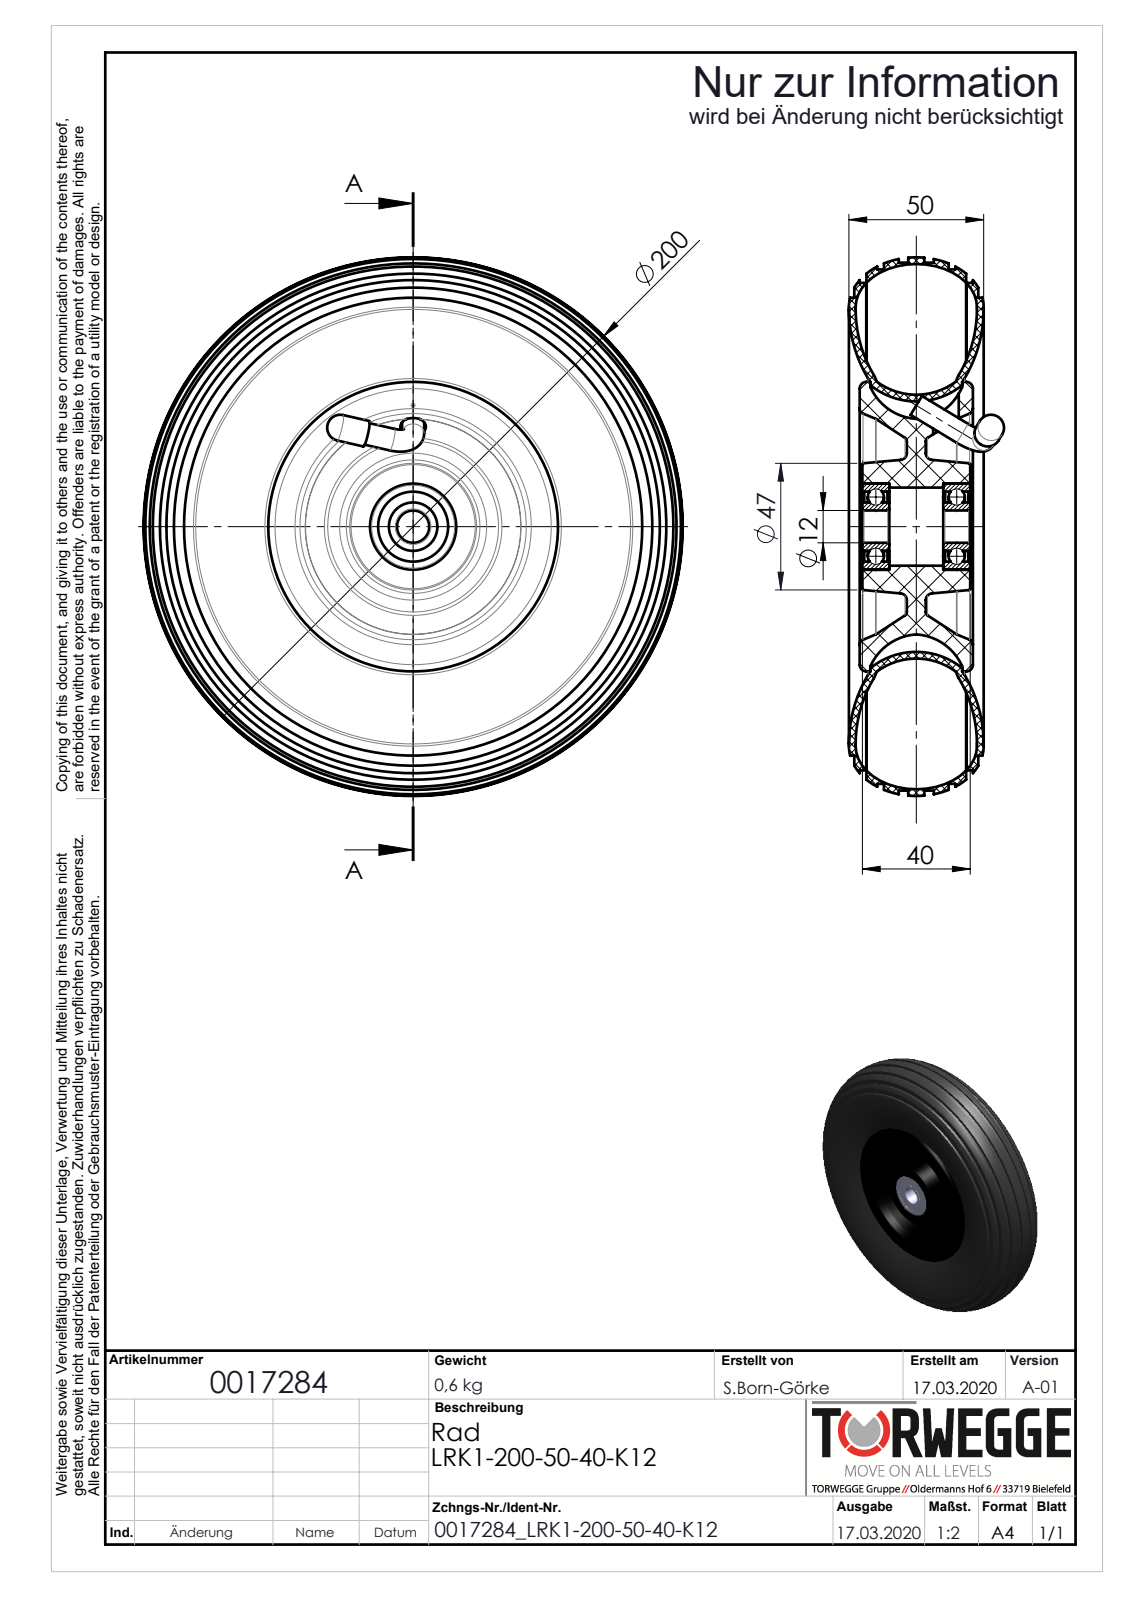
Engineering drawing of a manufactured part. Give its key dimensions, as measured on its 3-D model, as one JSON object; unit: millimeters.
{"part_name": "0017284", "step_written_by": "SolidWorks 2018 (AUTOMOTIVE_DESIGN)", "units": "millimeters", "bodies": {"solids": 10, "faces": 236, "planar": 46, "cylindrical": 74, "other": 116}, "overall_size": [200, 200, 57.56], "volume_mm3": 323613, "surface_area_mm2": 215936, "round_holes": [[9.5, 1], [12, 1], [18, 1], [26, 1], [29, 1], [32, 1]], "round_bosses_or_shafts": [[8.2, 2], [196, 1], [191, 1], [181, 1], [170, 1], [107.5, 1], [9.7, 1]], "face_to_face_distances": [2.5, 6.5, 3, 9, 26.5, 2, 44, 11, 33, 15]}
